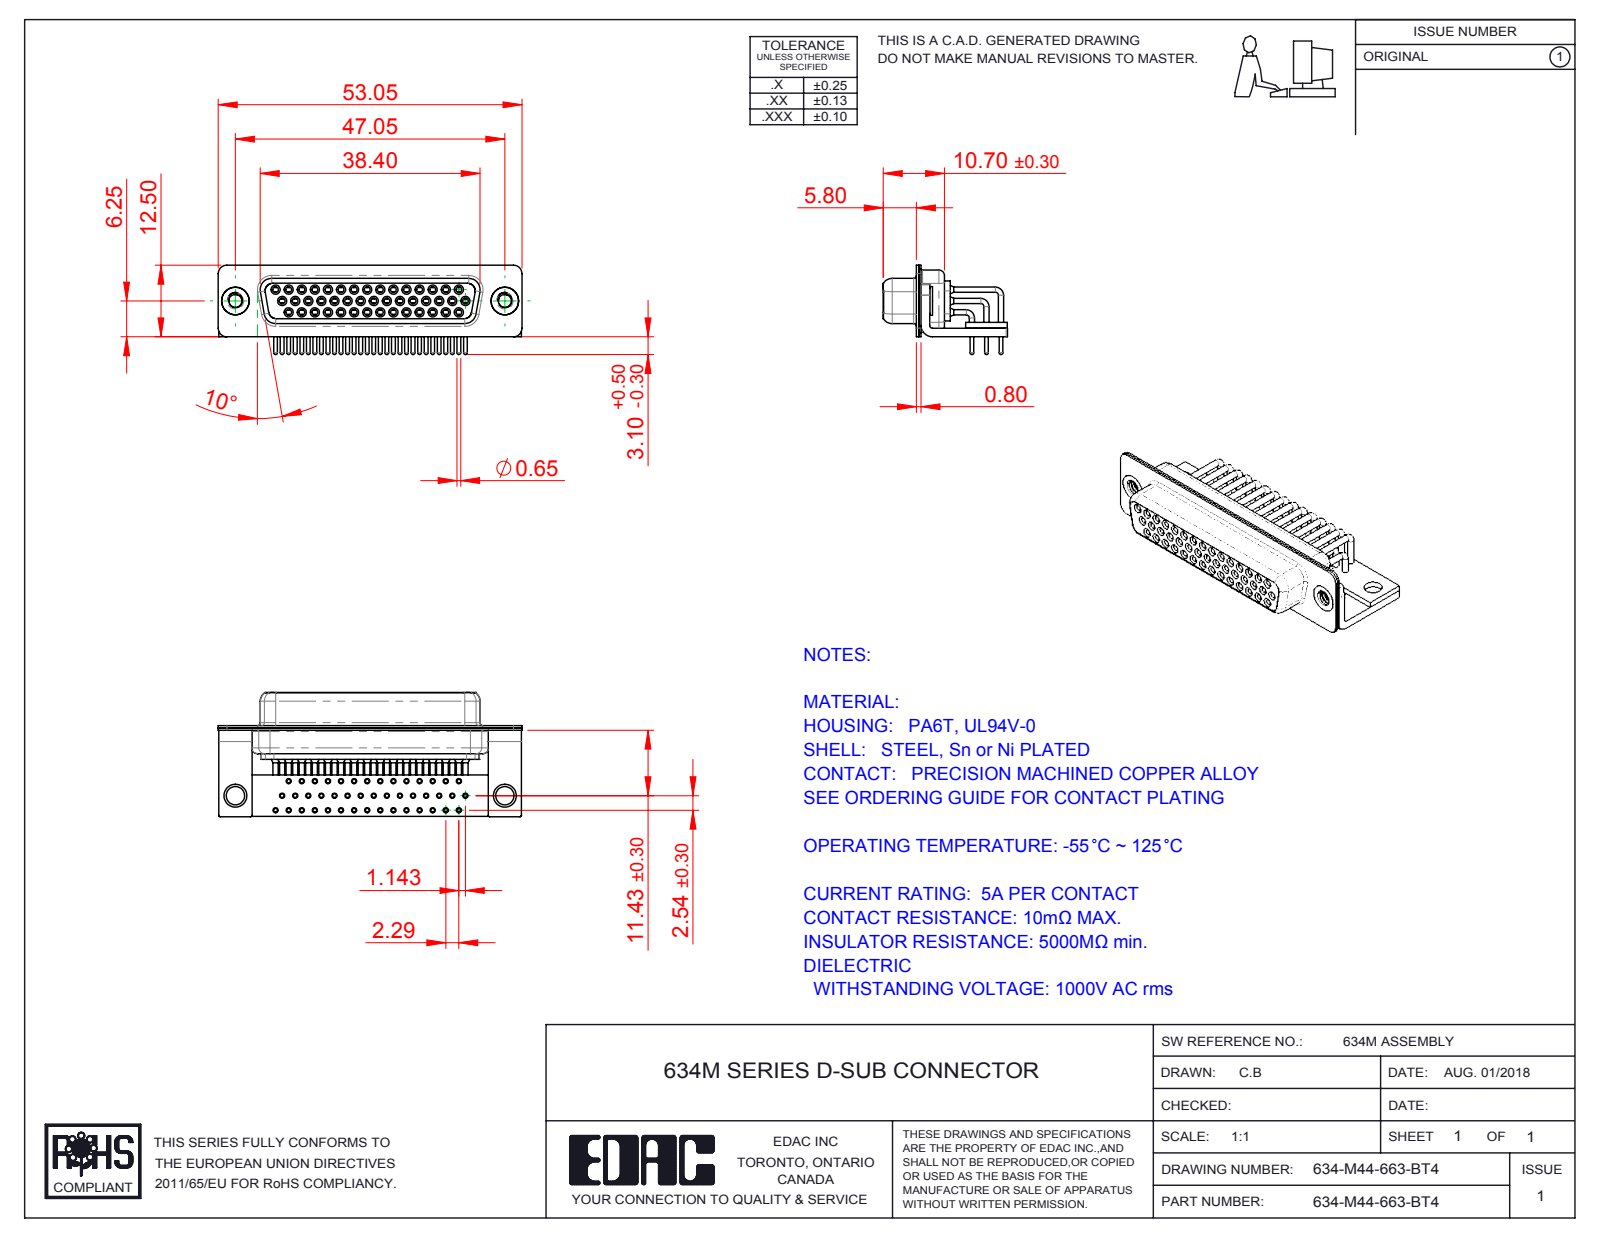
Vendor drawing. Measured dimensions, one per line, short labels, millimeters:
name: 634M Housing_44 Contacts; 634M 4-40 Threaded Rivet_Stabilizer; 634M Contact Row 2; 634M Contact Row 3 (+6 more)
written by: SolidWorks 2016 (CONFIG_CONTROL_DESIGN)
unit: mm
bodies: 52 solids, 2749 faces (753 planar, 1259 cylindrical, 737 other)
size: 53.05 × 21.7 × 15.6
volume: 4 457 mm³; area: 14 593 mm²
holes: 44× ⌀0.9, 44× ⌀1, 44× ⌀1.1, 44× ⌀1.7, 44× ⌀1.8, 44× ⌀2, 2× ⌀2.26, 2× ⌀3.2, 2× ⌀4, 2× ⌀4.8
bosses: 44× ⌀1.6, 44× ⌀1.5, 44× ⌀0.9, 44× ⌀0.65, 2× ⌀5, 2× ⌀4.9
rounds: 16× R0.25, 16× R1.5, 13× R2, 8× R1.35, 8× R1.6, 5× R0.5, 4× R0.6, 4× R0.65
face distances: 0.4, 2.3, 1, 1.9, 0.8, 9.35, 1.45, 8.95, 0.85, 8.5
hole spacings: 2.28, 2.29, 4.57, 6.86, 11.43, 3.96, 8.24, 9.14
